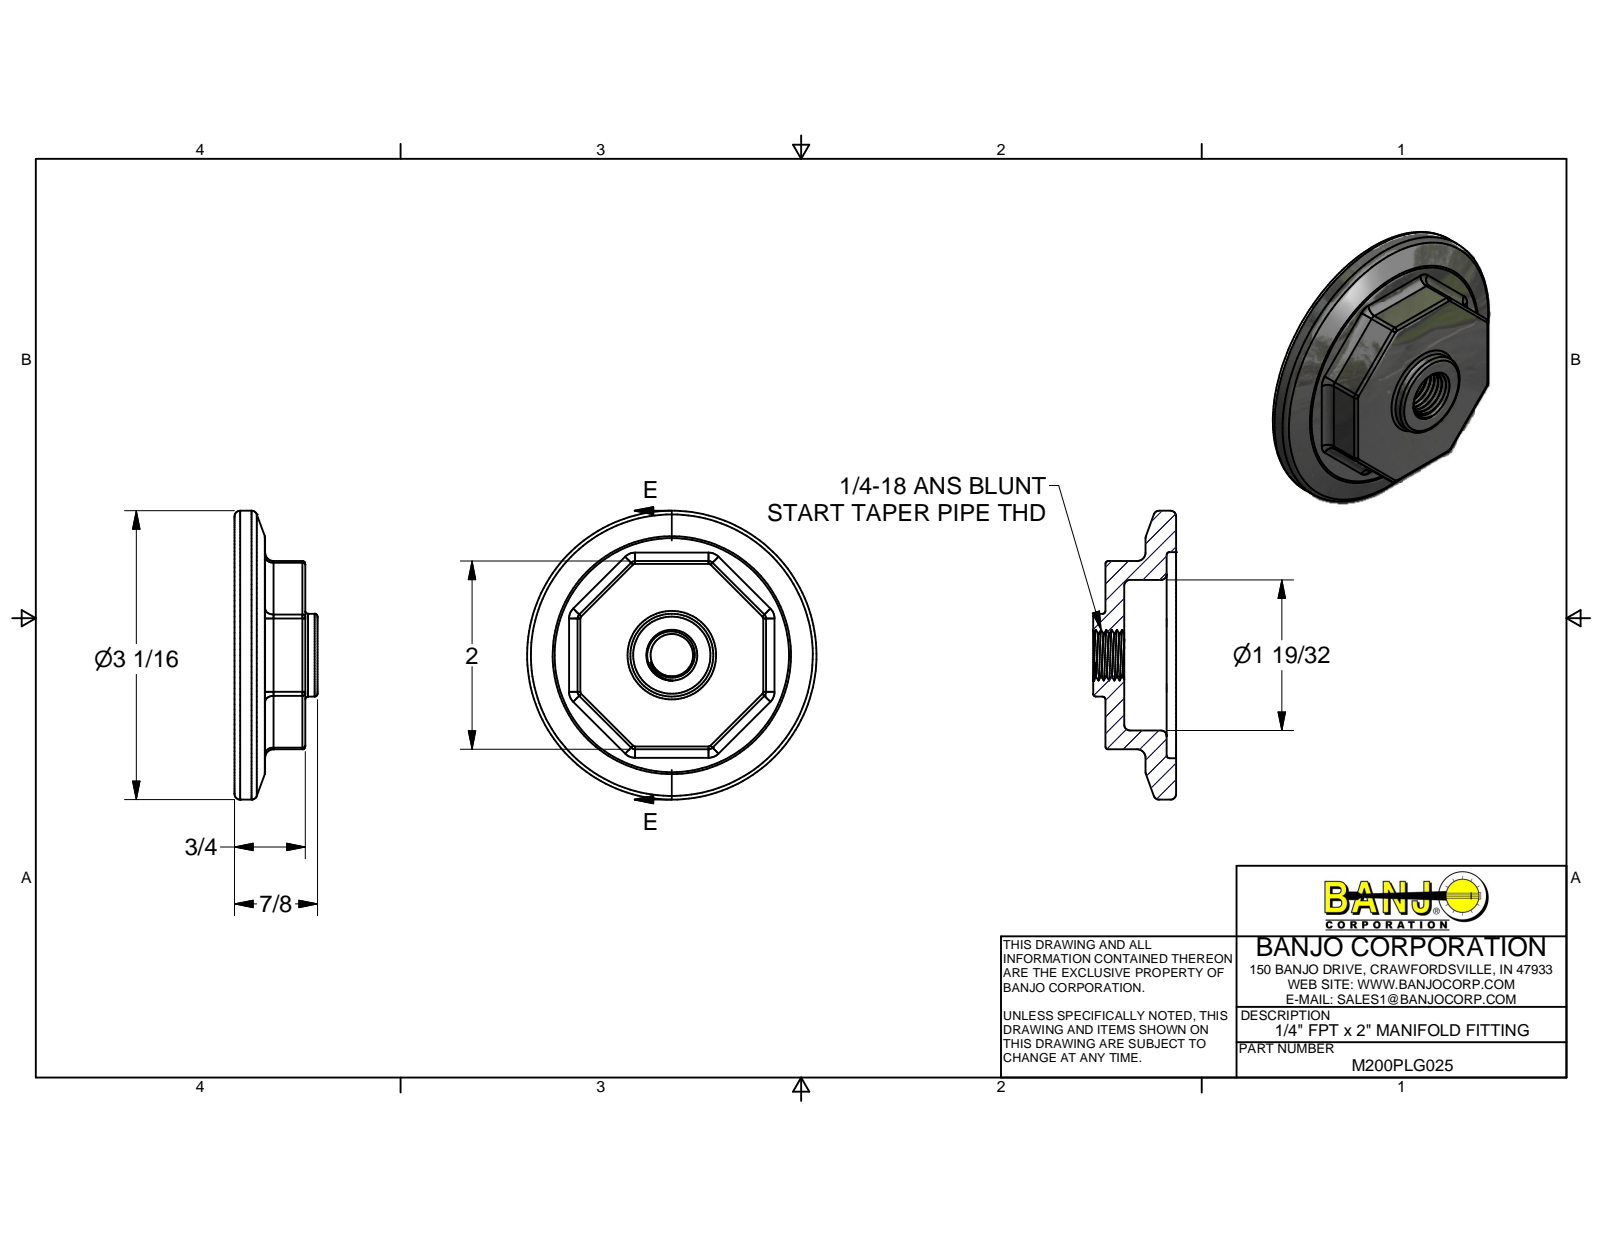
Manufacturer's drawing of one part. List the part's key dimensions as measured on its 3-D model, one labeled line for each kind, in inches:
Part name (STEP PRODUCT): M200PLG025
STEP written by: Autodesk Inventor 2014 (AUTOMOTIVE_DESIGN)
Units: inches
Bodies: 1 solid, 117 faces (23 planar, 52 cylindrical, 42 other)
Overall size (bounding box): 3.07 × 3.07 × 0.88
Volume: 2.366 in³ · Surface area: 22.75 in²
Round holes (diameter × count): ⌀0.451 ×1, ⌀2.19 ×1
Round bosses / shafts (diameter × count): ⌀3.07 ×1, ⌀0.88 ×1
Partial cylindrical surfaces — rounded edges, fillets, slot ends (radius × count): R0.06 ×32, R0.03 ×8, R0.09 ×8
Main face-to-face distances: 0.2, 0.75, 0.55, 1.8, 0.1, 0.65, 0.45, 2, 0.426, 0.226
